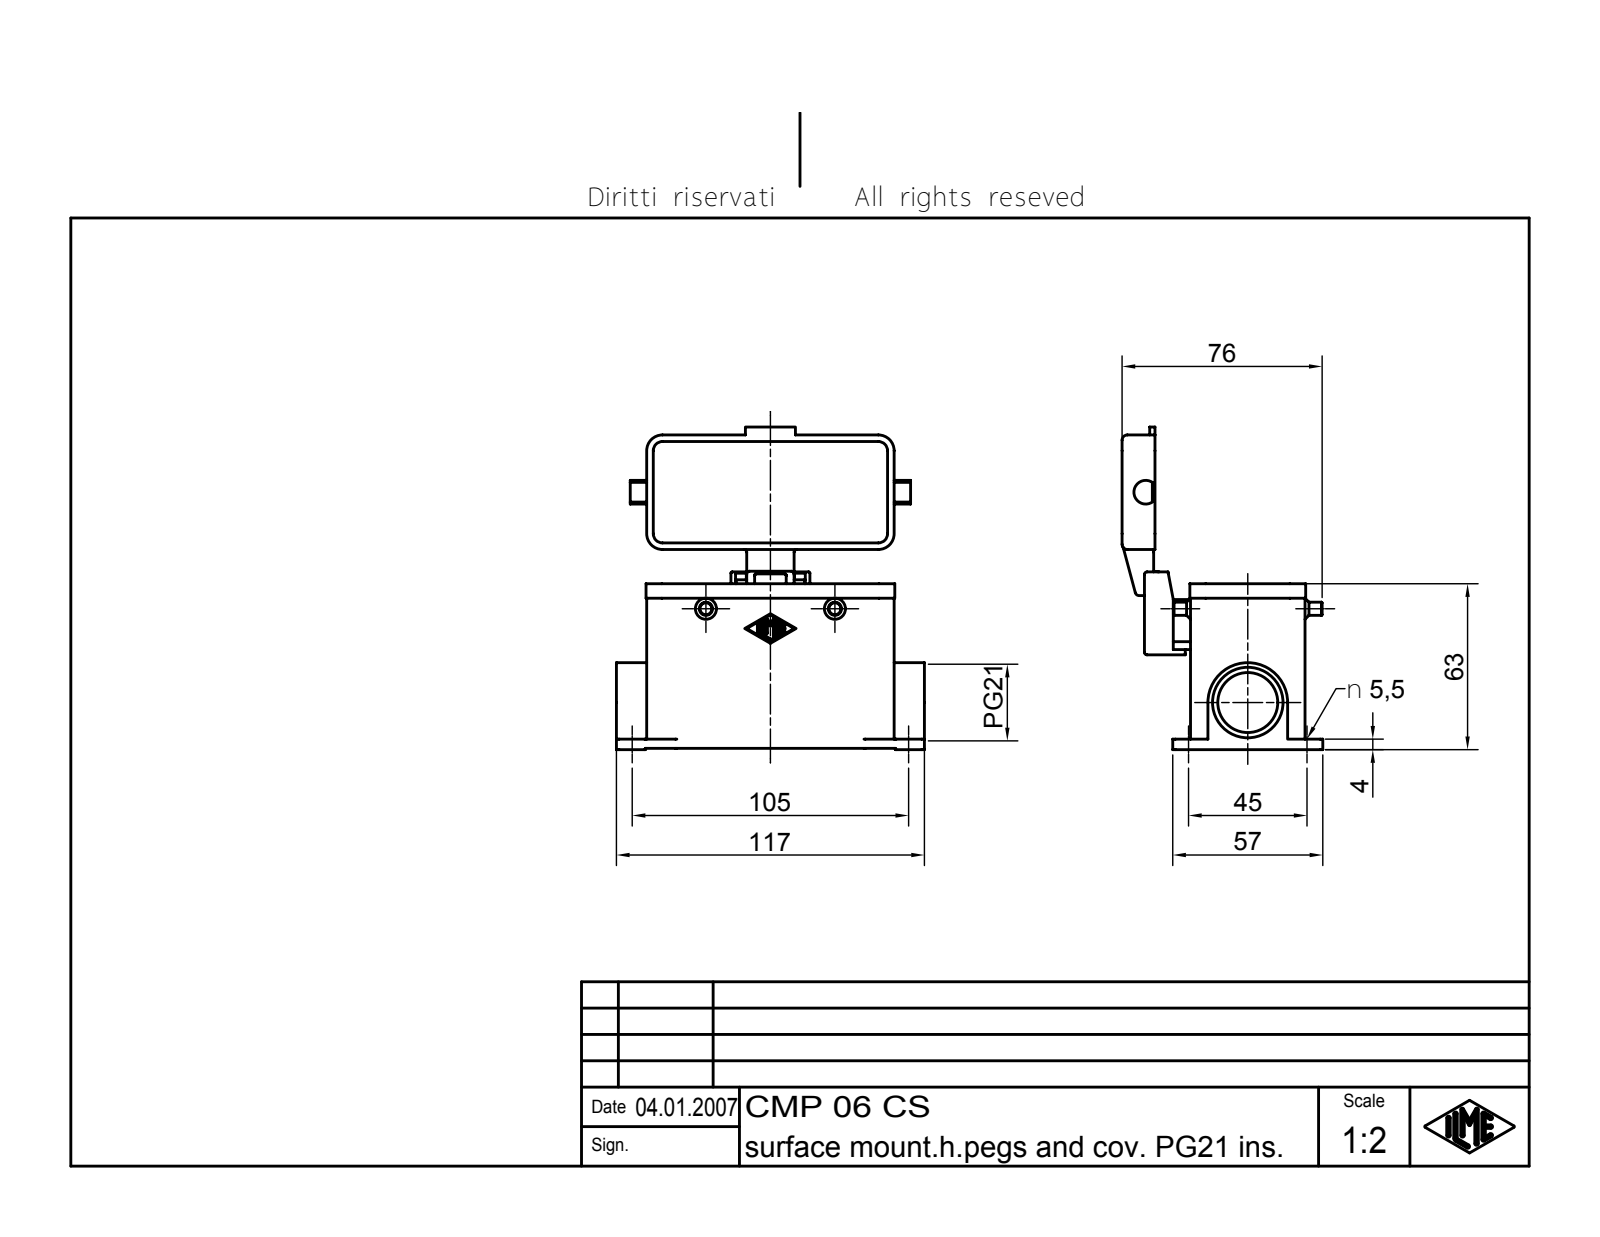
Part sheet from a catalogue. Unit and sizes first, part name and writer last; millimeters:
Units: millimetres
Overall size (bounding box): 122.5 × 117 × 76.25
Round holes (diameter × count): ⌀5.5 ×4, ⌀4 ×1, ⌀5 ×1, ⌀22.78 ×1, ⌀26.78 ×1
Round bosses / shafts (diameter × count): ⌀5 ×2, ⌀3 ×2, ⌀7 ×1, ⌀4 ×1
Partial cylindrical surfaces — rounded edges, fillets, slot ends (radius × count): R1 ×26, R0.38 ×14, R6 ×12, R0.5 ×9, R0.7 ×8, R2 ×8, R3 ×4, R3.5 ×4
Main face-to-face distances: 3, 40.5, 3.5, 43.5, 29, 63, 37.5, 22.5, 69.5, 66.5
Hole centre spacings: 45, 105, 114.24
Volume: 117 309 mm³ · Surface area: 66 261 mm²
Bodies: 2 solids, 475 faces (177 planar, 177 cylindrical, 121 other)
Part name (STEP PRODUCT): CMP 06 CS
STEP written by: Autodesk Inventor 7 (AUTOMOTIVE_DESIGN)
